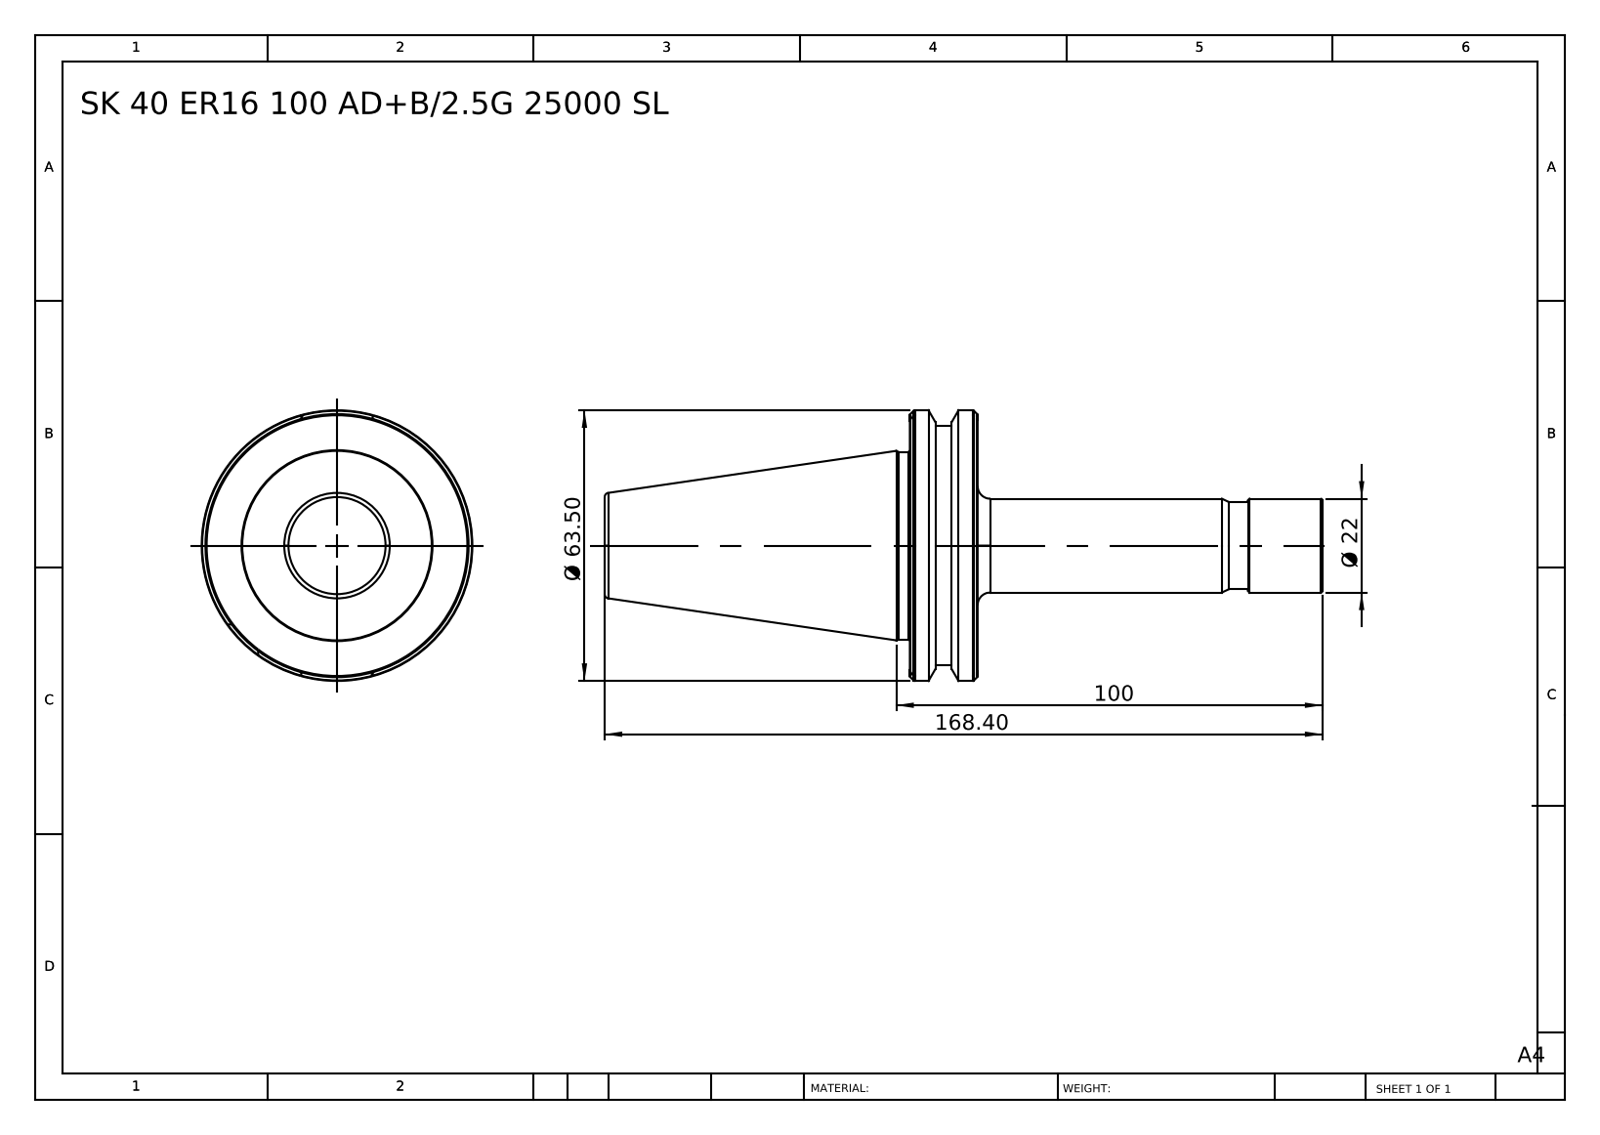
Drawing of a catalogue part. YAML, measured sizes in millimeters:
part_name: "SK40 ER16M 100 AD+B 2.5G 25000 SL"
step_written_by: "SolidWorks 2014 (CONFIG_CONTROL_DESIGN)"
units: millimeters
bodies: {solids: 1, faces: 77, planar: 7, cylindrical: 14, other: 56}
overall_size: [168.4, 63.5, 63.5]
volume: 147704
surface_area: 22449
round_bosses_or_shafts:
  - {diameter: 63.5, count: 1}
  - {diameter: 56, count: 1}
  - {diameter: 44, count: 1}
  - {diameter: 22, count: 1}
  - {diameter: 20.4, count: 1}
face_to_face_distances: [15.9, 87.5, 71.6, 80.9, 96.8, 168.4, 90.8, 9.9, 6, 77.6]
